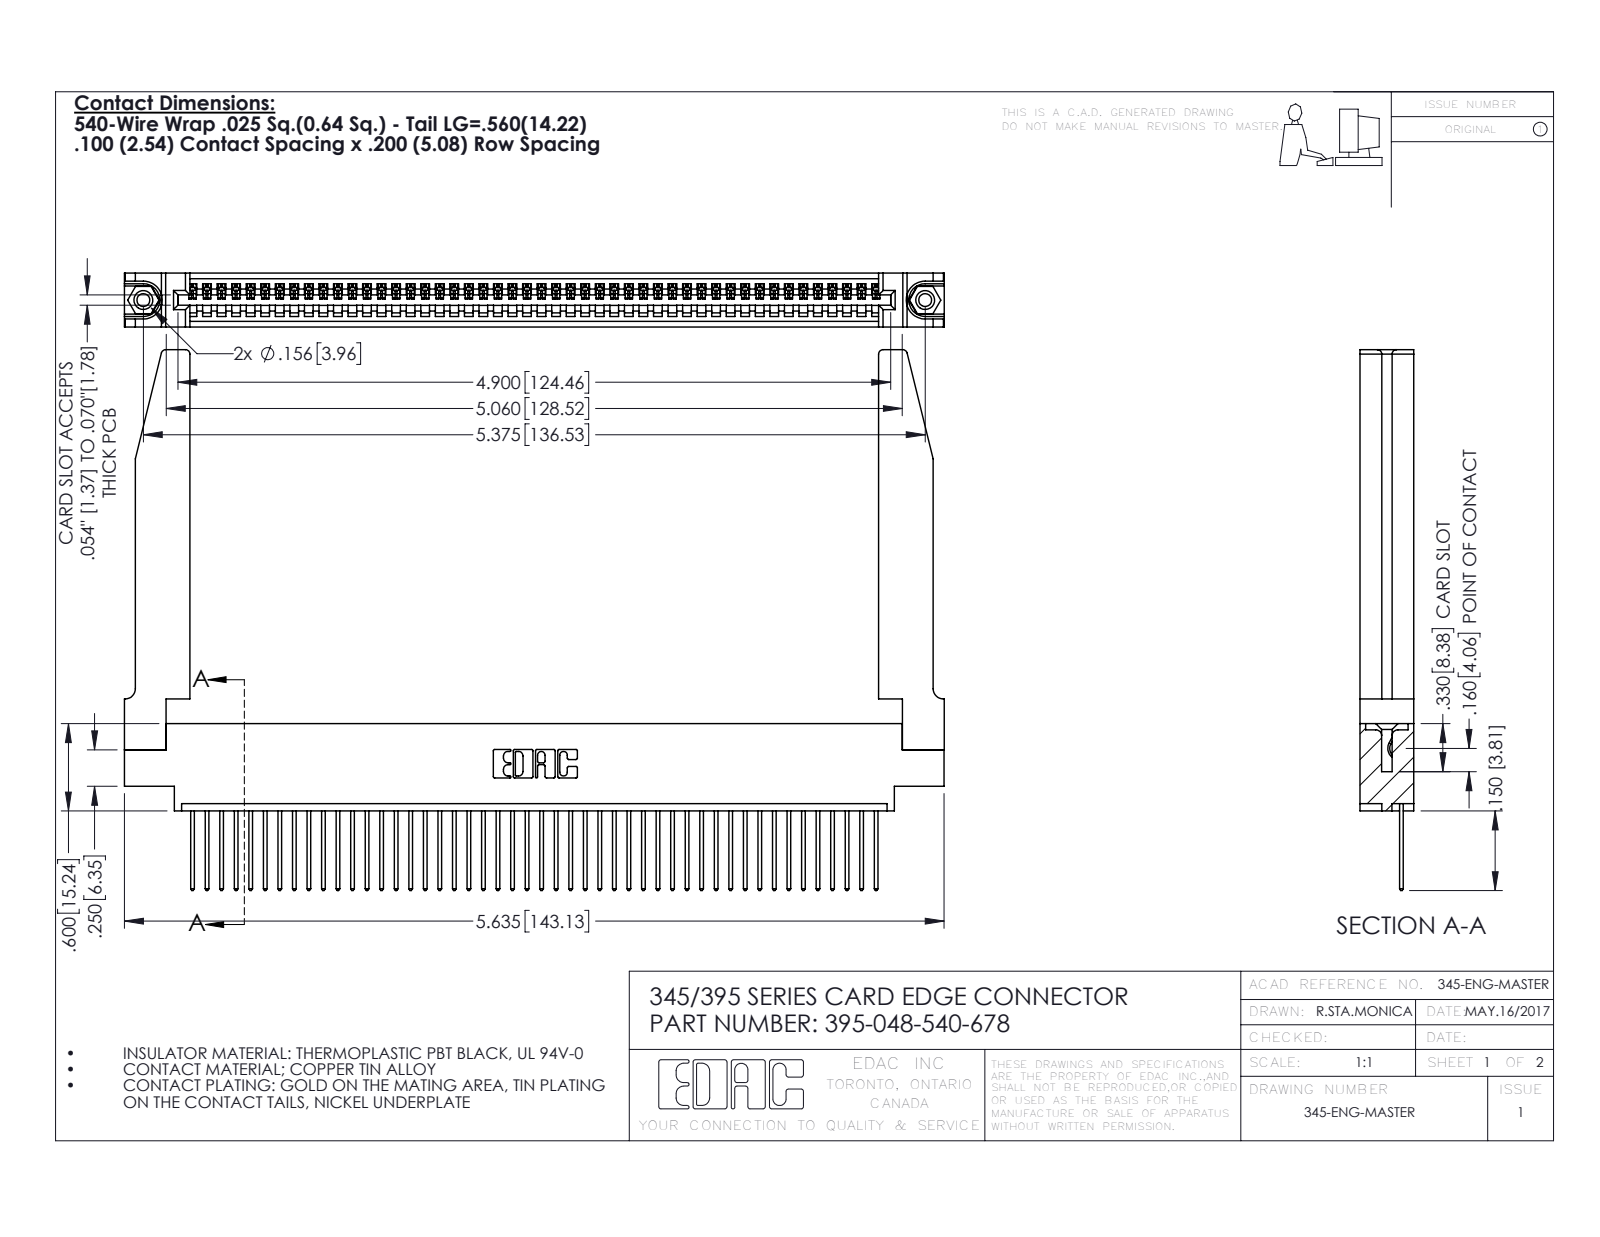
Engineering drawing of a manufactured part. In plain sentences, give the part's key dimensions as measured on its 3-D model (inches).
The part is named "395-048-540-678; 345-250-001_345-250-001-102; 345-220-078_345-220-078; 345-292-001_345-293-140 (+1 more)". Its 3-D file was written by "SolidWorks 2016 (CONFIG_CONTROL_DESIGN)". It is 53 solids with 3148 faces: 2146 planar, 950 cylindrical and 52 other. Overall it measures 5.636 by 3.717 by 0.37 inches. Its volume is 1.304 cubic inches and its surface area 39.67 square inches. Round holes: 2 of diameter 0.089, 2 of diameter 0.125, 2 of diameter 0.156, 1 of diameter 0.064. Round bosses or shafts: 2 of diameter 0.155. Partial cylindrical surfaces (rounded edges, fillets, slot ends): 96 of radius 0.006, 96 of radius 0.01, 22 of radius 0.01, 8 of radius 0.03, 6 of radius 0.007, 6 of radius 0.031, 3 of radius 0.026, 2 of radius 0.031. The main face-to-face distances are 0.37, 0.072, 0.298, 0.098, 0.272, 0.025, 0.2, 0.225, 0.15, 0.148. The hole center spacings are 0.27, 5.139, 5.375.
